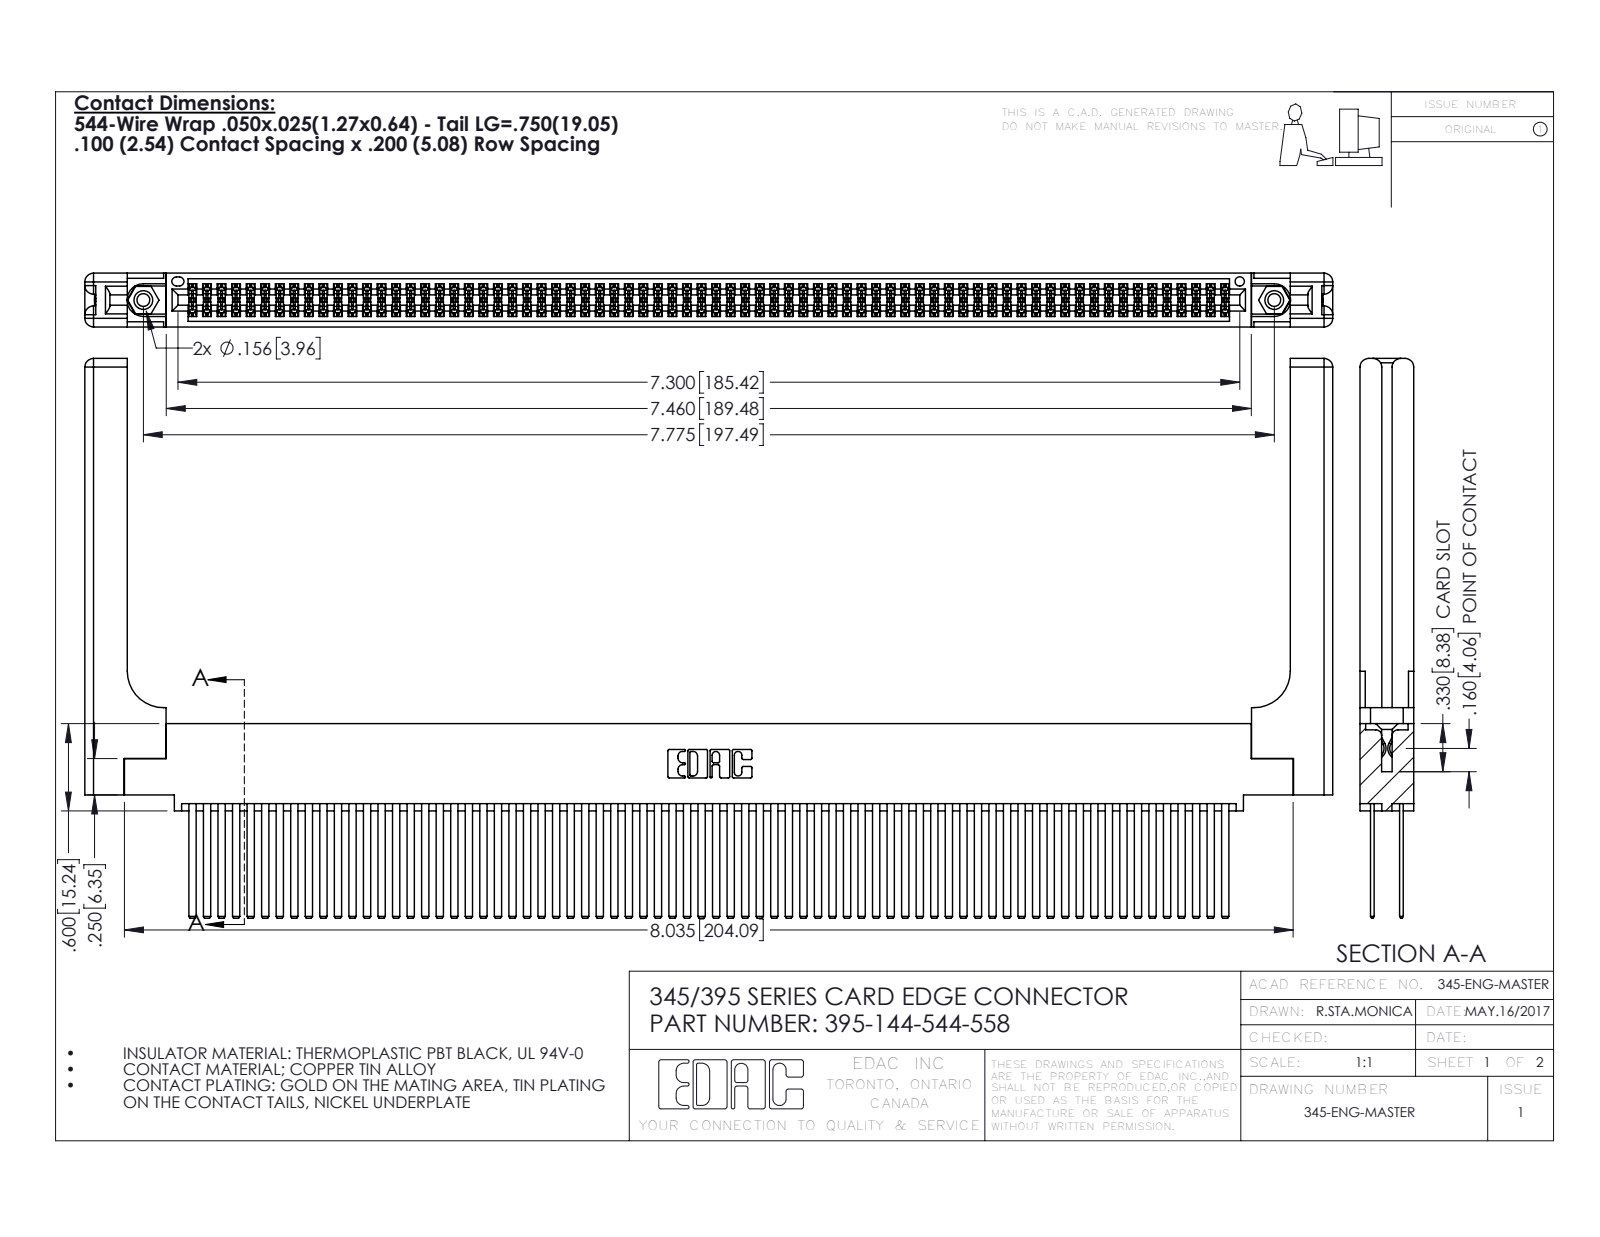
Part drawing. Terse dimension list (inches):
name: 345-220-058_345-220-058; 395-144-544-558; 345-250-001_345-250-001-102; 345 Part_0.110 Offset - 0.156 Dia-TH (+1 more)
written by: SolidWorks 2016 (CONFIG_CONTROL_DESIGN)
unit: in
bodies: 149 solids, 6722 faces (4408 planar, 2254 cylindrical, 60 other)
size: 8.579 × 3.847 × 0.37
volume: 1.945 in³; area: 71.65 in²
holes: 2× ⌀0.089, 2× ⌀0.125, 2× ⌀0.156, 1× ⌀0.064
bosses: 2× ⌀0.155
rounds: 216× R0.006, 22× R0.01, 16× R0.06, 6× R0.007, 6× R0.031, 3× R0.026, 2× R0.014, 2× R0.019
face distances: 0.072, 0.298, 0.098, 0.272, 0.025, 0.2, 0.225, 0.37, 0.175, 0.148
hole spacings: 0.27, 7.539, 7.775
